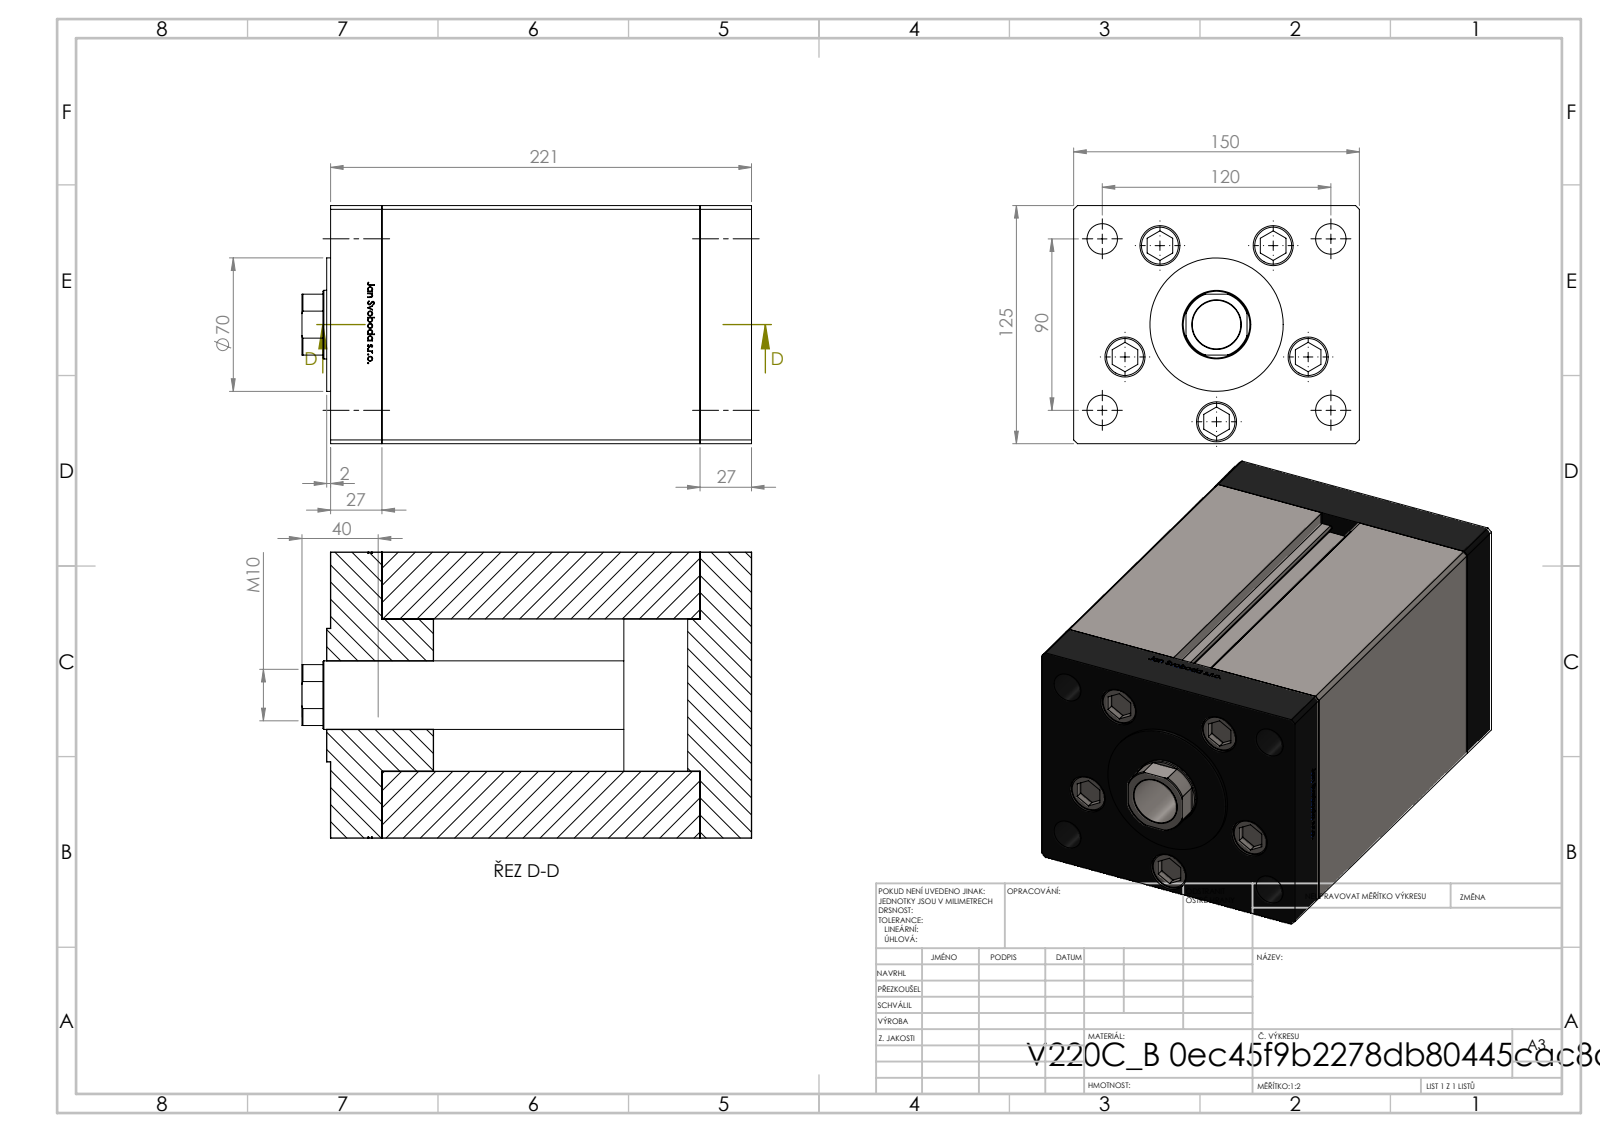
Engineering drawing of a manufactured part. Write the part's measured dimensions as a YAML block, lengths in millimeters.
part_name: "V220C_VC_B; V220C BACK_B; V220C_FRONT_B; ALLEN BOLT (+1 more)"
step_written_by: "SolidWorks 2019 (CONFIG_CONTROL_DESIGN)"
units: millimeters
bodies: {solids: 14, faces: 1185, planar: 464, cylindrical: 147, other: 574}
overall_size: [236, 150, 125]
volume: 3580000
surface_area: 367811
round_holes:
  - {diameter: 17.5, count: 5}
  - {diameter: 21, count: 5}
  - {diameter: 16, count: 4}
  - {diameter: 2, count: 2}
  - {diameter: 13.16, count: 2}
  - {diameter: 25.5, count: 1}
  - {diameter: 36, count: 1}
round_bosses_or_shafts:
  - {diameter: 8, count: 5}
  - {diameter: 80, count: 1}
  - {diameter: 70, count: 1}
partial_cylinders:
  - {radius: 0.93, count: 2}
  - {radius: 17.5, count: 1}
face_to_face_distances: [27, 194, 125, 167, 150, 33.5, 221, 6.5, 160.5, 187.5]
hole_center_spacings: [51, 75, 30.43, 30.48, 58.89, 60.3, 61.25, 63.14]
